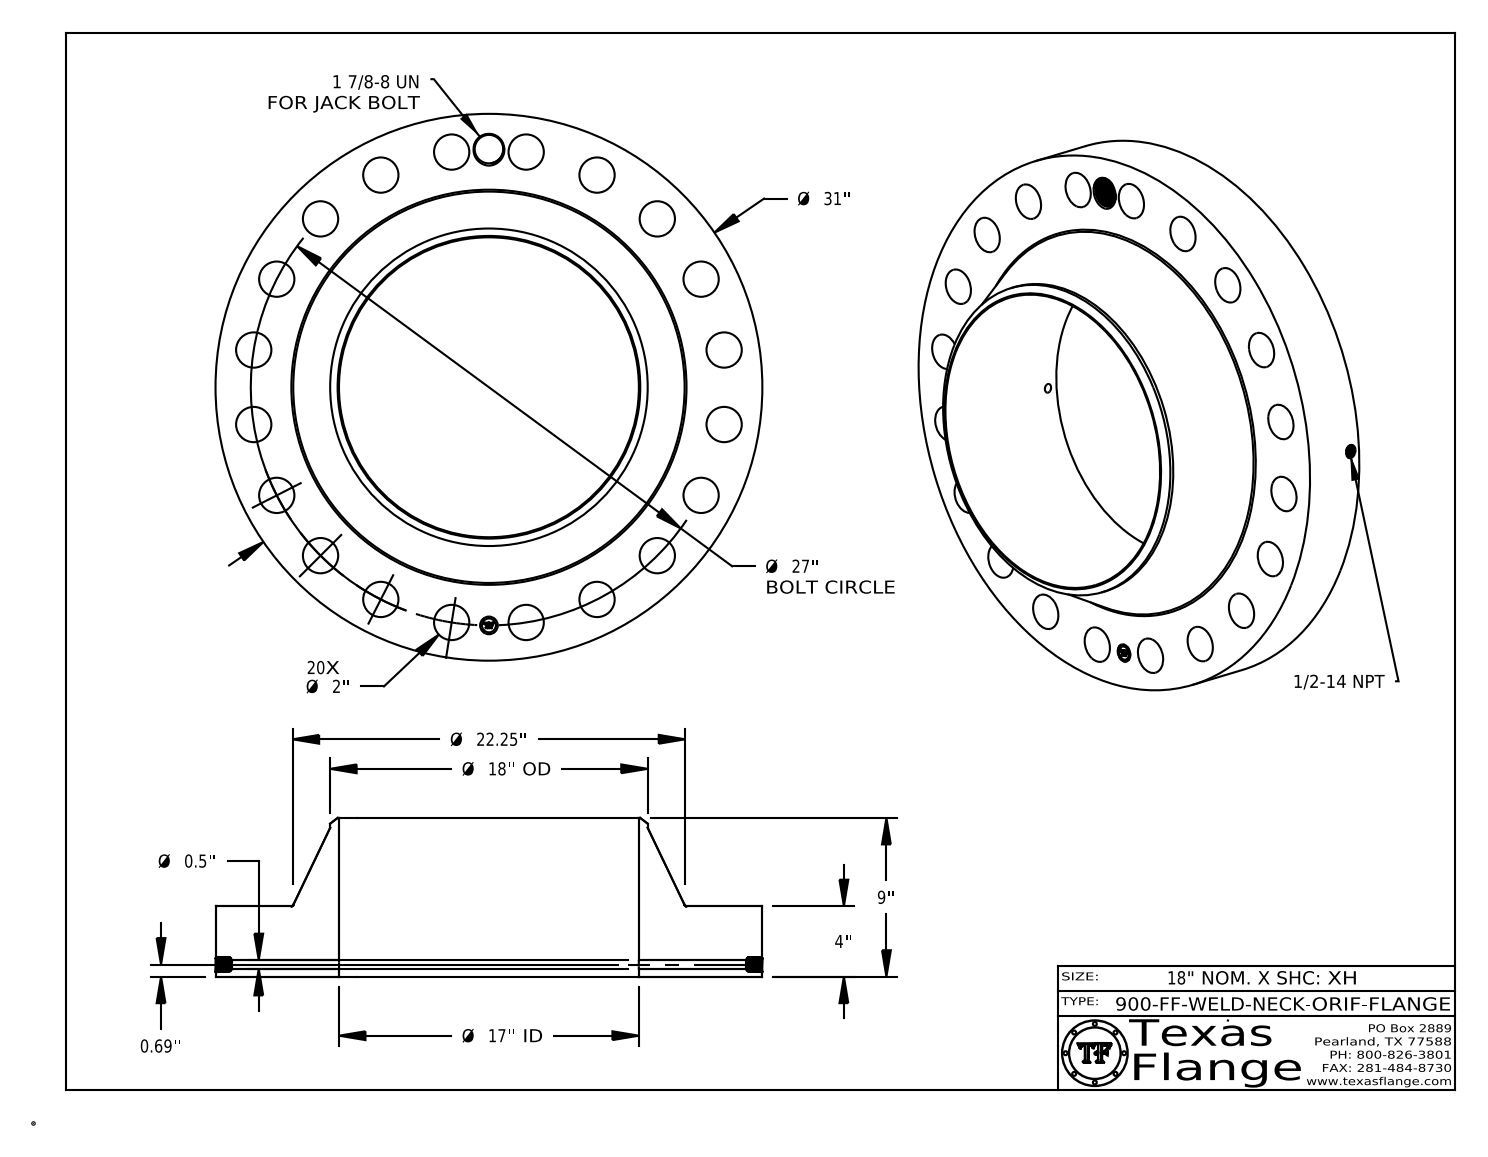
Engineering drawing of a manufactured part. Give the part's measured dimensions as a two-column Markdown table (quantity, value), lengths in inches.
| quantity | value |
| --- | --- |
| part name | 900-FF-WELD-NECK |
| STEP written by | CATIA V5 STEP AP214 (AUTOMOTIVE_DESIGN) |
| units | inches |
| bodies | 1 solid, 892 faces (368 planar, 149 cylindrical, 375 other) |
| overall size | 31 × 31 × 9 |
| volume | 2 269 in³ |
| surface area | 2 569 in² |
| round holes (diameter × count) | 2 × 20, 0.5 × 1, 0.672 × 1, 1 × 1, 1.615 × 1, 17 × 1 |
| round bosses / shafts (diameter × count) | 0.061 × 8, 31 × 1, 18 × 1, 0.788 × 1 |
| main face-to-face distances | 4, 9, 5, 3.985, 0.015, 5.015, 0.298, 0.293, 0.054, 0.248 |
| hole center spacings | 13.5, 19.092, 25.679, 26.668, 12.258, 4.224, 8.344, 15.87 |
